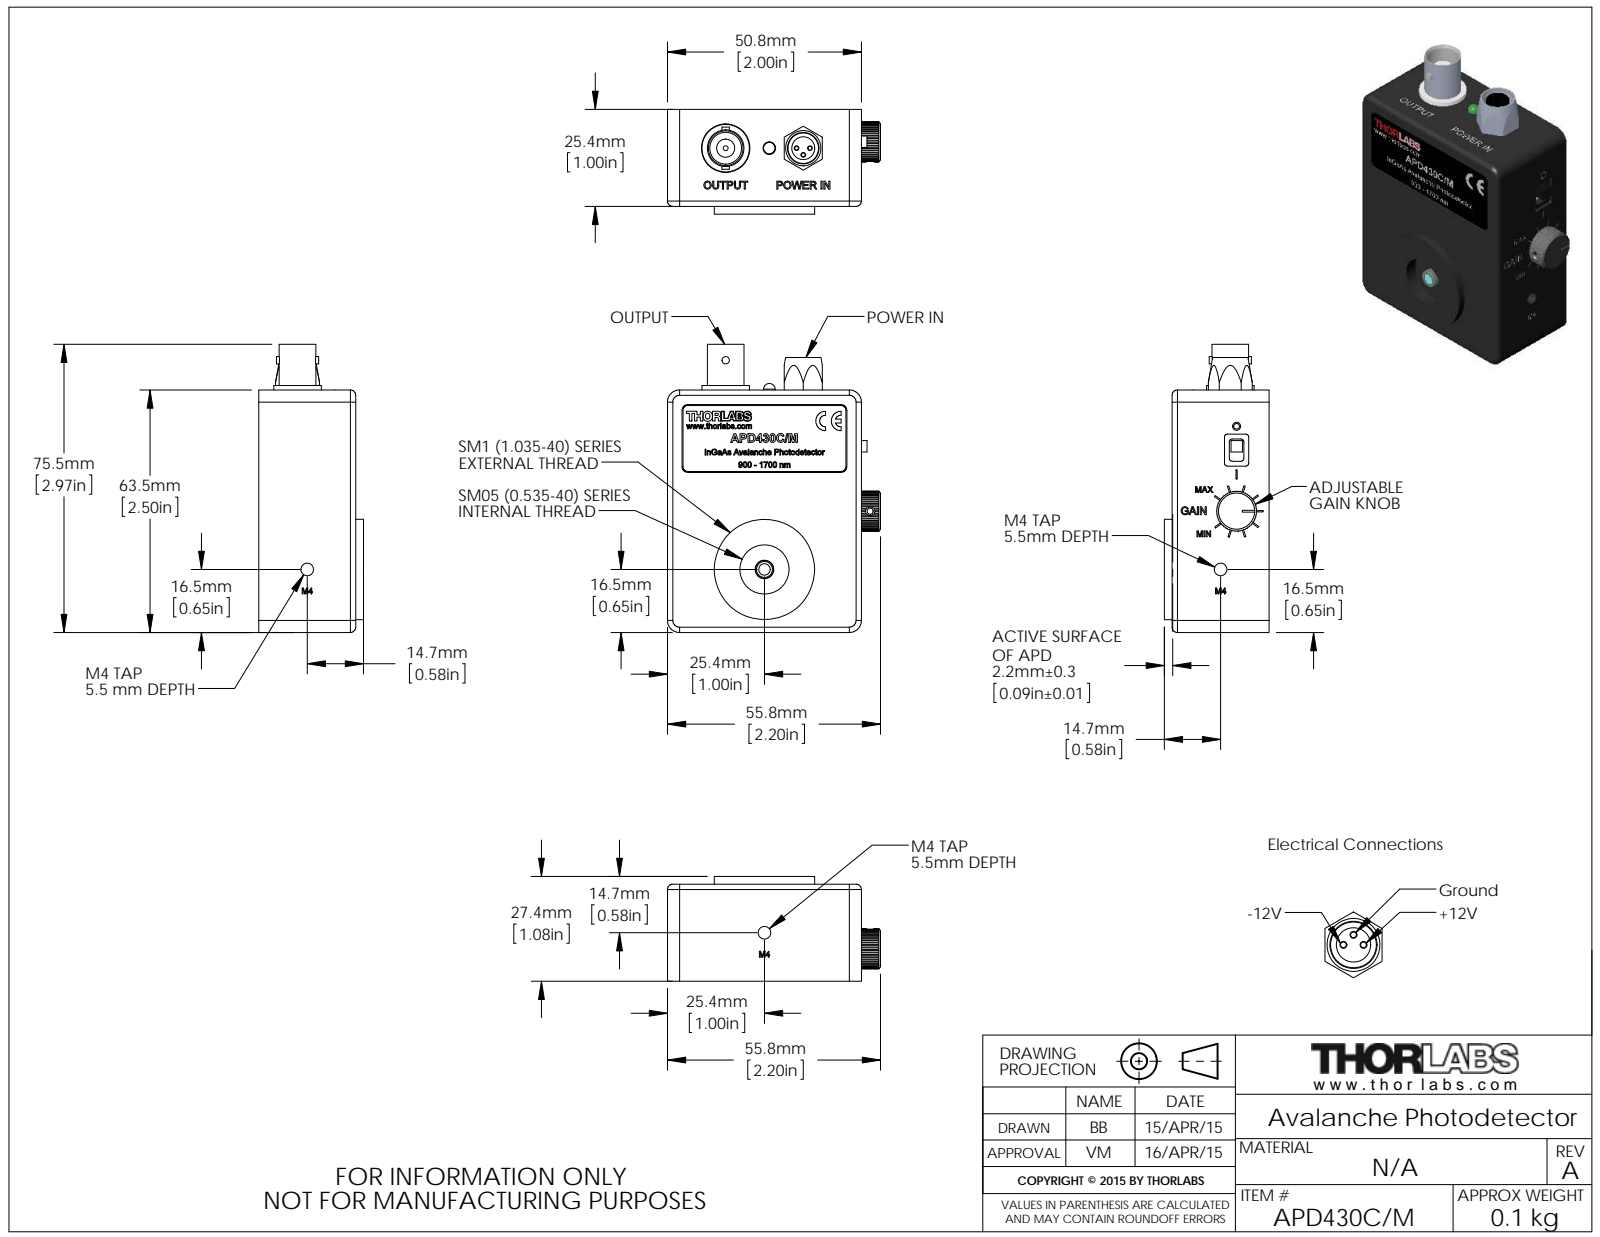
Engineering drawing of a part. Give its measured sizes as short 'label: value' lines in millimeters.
name: APD430x-Folie_APD430C-M; M0092-0927-bzw-0928_Gehäuse_APD4xx_M0092-0927 Rev A metrisch; M0092-0923 Drehknopf verstellbarer Gain APD4xx_Mit Laserbeschriftung; flat head screw_am_B18.6.7M - M2 x 0.4 x 4 Type I Cross Recessed FHMS --4N (+8 more)
written by: SolidWorks 2014 (AUTOMOTIVE_DESIGN)
unit: mm
bodies: 4 solids, 2462 faces (1319 planar, 472 cylindrical, 671 other)
size: 75.46 × 55.8 × 27.43
volume: 32 213 mm³; area: 34 492 mm²
holes: 9× ⌀1.6, 6× ⌀0.51, 6× ⌀0.81, 4× ⌀2.4, 4× ⌀2.44, 3× ⌀0.46, 2× ⌀0.45, 2× ⌀2.5, 2× ⌀3.3, 1× ⌀1.27, 1× ⌀1.32, 1× ⌀2.1
bosses: 5× ⌀1, 4× ⌀3.8, 4× ⌀2, 2× ⌀1.64, 2× ⌀1.6, 2× ⌀1.3, 1× ⌀26.29, 1× ⌀12.45
rounds: 53× R0.3, 19× R3.17, 14× R3.3, 10× R0.8, 8× R0.79, 8× R2.41, 6× R0.5, 6× R1.91
face distances: 1.59, 13.08, 11.49, 2.54, 11.48, 9.89, 1.6, 0.4, 23.81, 10.67
hole spacings: 41.17, 2.54, 20.89, 39.38, 4.41, 16.46, 21.35, 51.14
